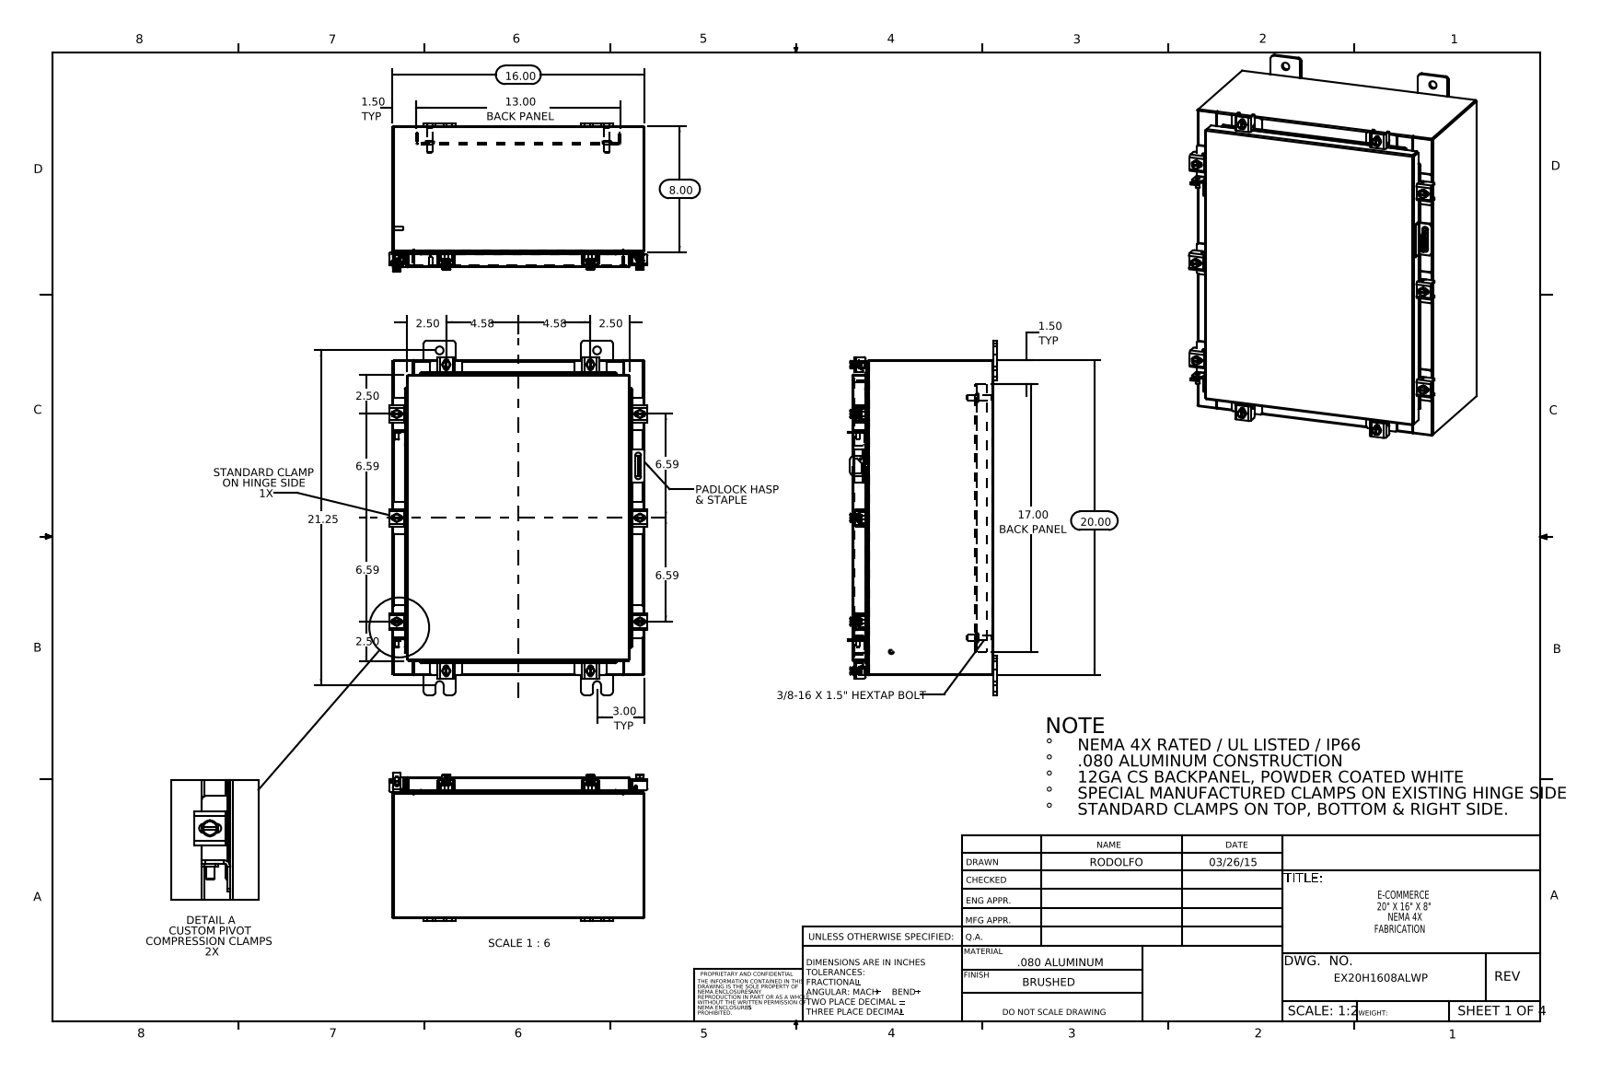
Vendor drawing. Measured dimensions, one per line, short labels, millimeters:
name: EX20H1608ALWP Padlock Staple; N-WMT04X30402202210-00 22104005_DEFAULT; EX20H1608ALWP; EX20H1608ALWP Special Clamp (+8 more)
written by: SolidWorks 2014 (CONFIG_CONTROL_DESIGN)
unit: mm
bodies: 71 solids, 1784 faces (955 planar, 685 cylindrical, 144 other)
size: 571.5 × 417.1 × 240.1
volume: 2 219 000 mm³; area: 2 197 000 mm²
holes: 10× ⌀5.4, 10× ⌀6.6, 8× ⌀12.7, 1× ⌀3.2, 1× ⌀6.4
bosses: 10× ⌀12.7, 10× ⌀6.4, 8× ⌀10.1, 4× ⌀15.9, 4× ⌀9.5, 4× ⌀8.4, 2× ⌀8, 2× ⌀6
rounds: 46× R1.5, 24× R0.3, 24× R4.8, 22× R2.2, 20× R3.6, 18× R3, 16× R2.3, 16× R2.5
face distances: 1.9, 226.1, 404.5, 228, 224.2, 506.1, 2.6, 25.4, 27.3, 198.8
hole spacings: 59.6, 112.8, 167.5, 259.6, 322.5, 365.1, 398.3, 422.1
